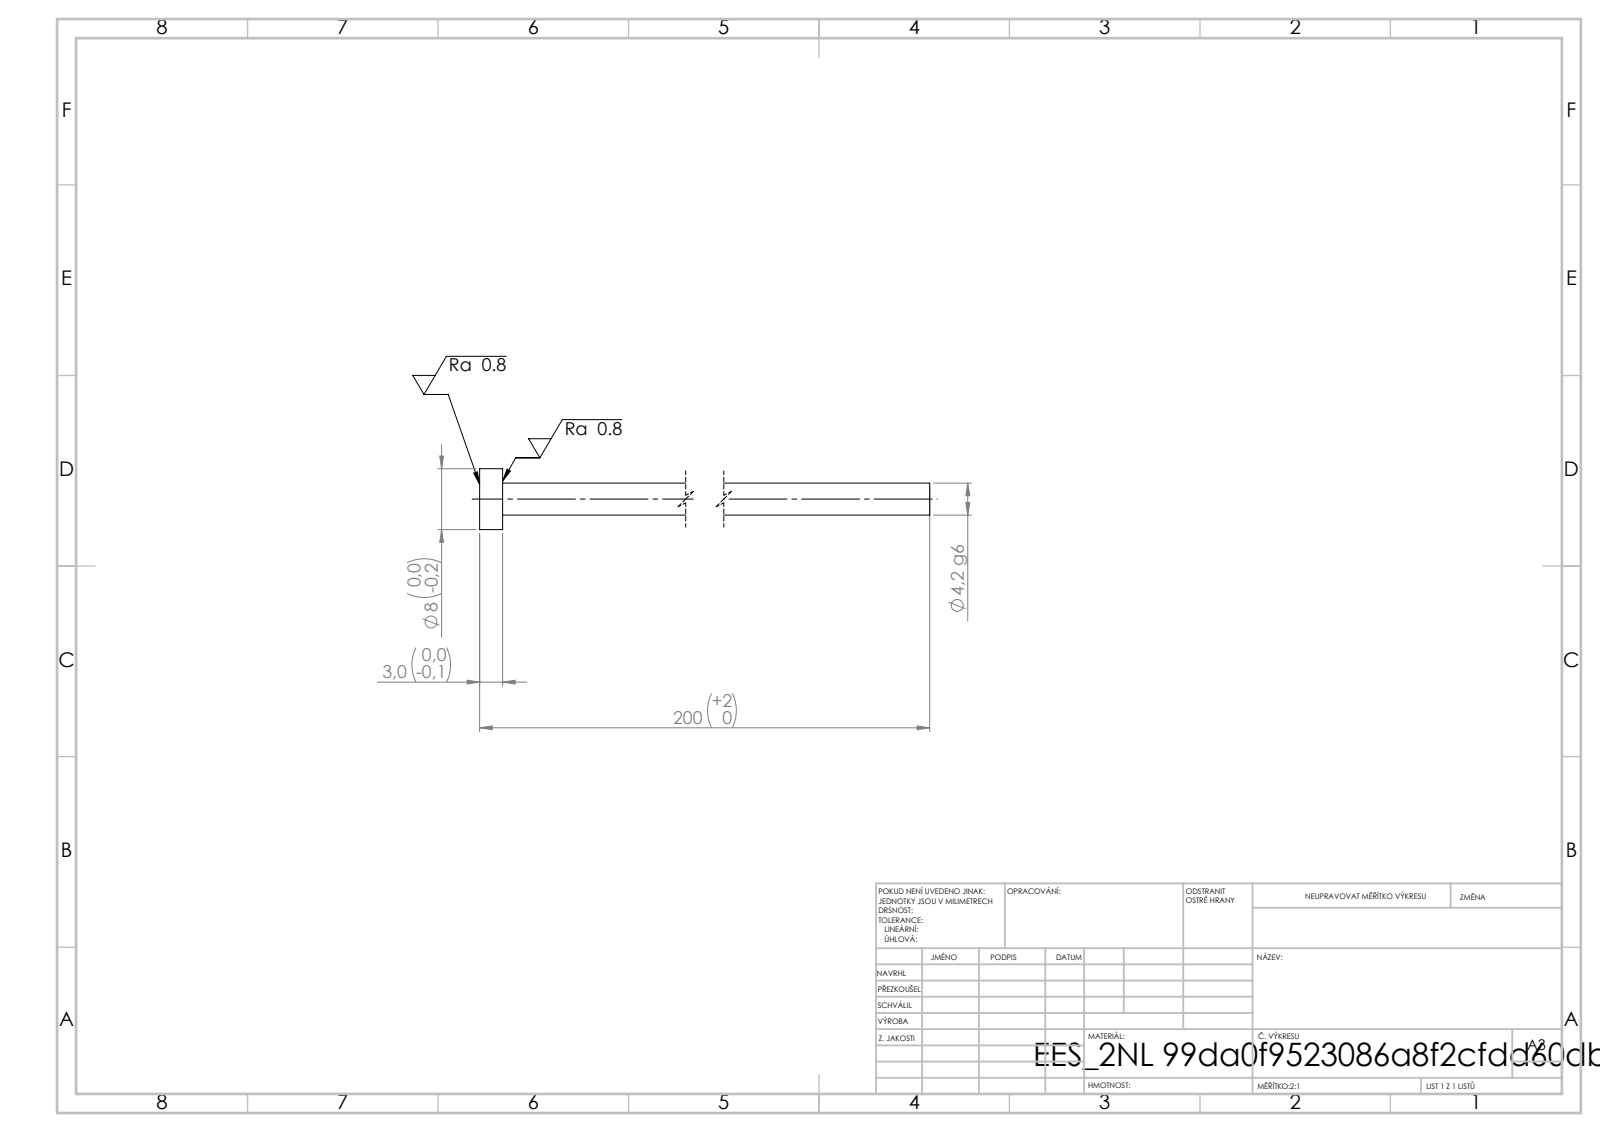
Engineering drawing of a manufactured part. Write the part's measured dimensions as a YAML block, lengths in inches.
step_written_by: "SolidWorks 2019 (CONFIG_CONTROL_DESIGN)"
units: inches
bodies: {solids: 1, faces: 7, planar: 3, cylindrical: 4, other: 0}
overall_size: [7.874, 0.315, 0.315]
volume: 0.176
surface_area: 4.301
round_bosses_or_shafts:
  - {diameter: 0.315, count: 1}
  - {diameter: 0.165, count: 1}
face_to_face_distances: [0.118, 7.874, 7.756]
